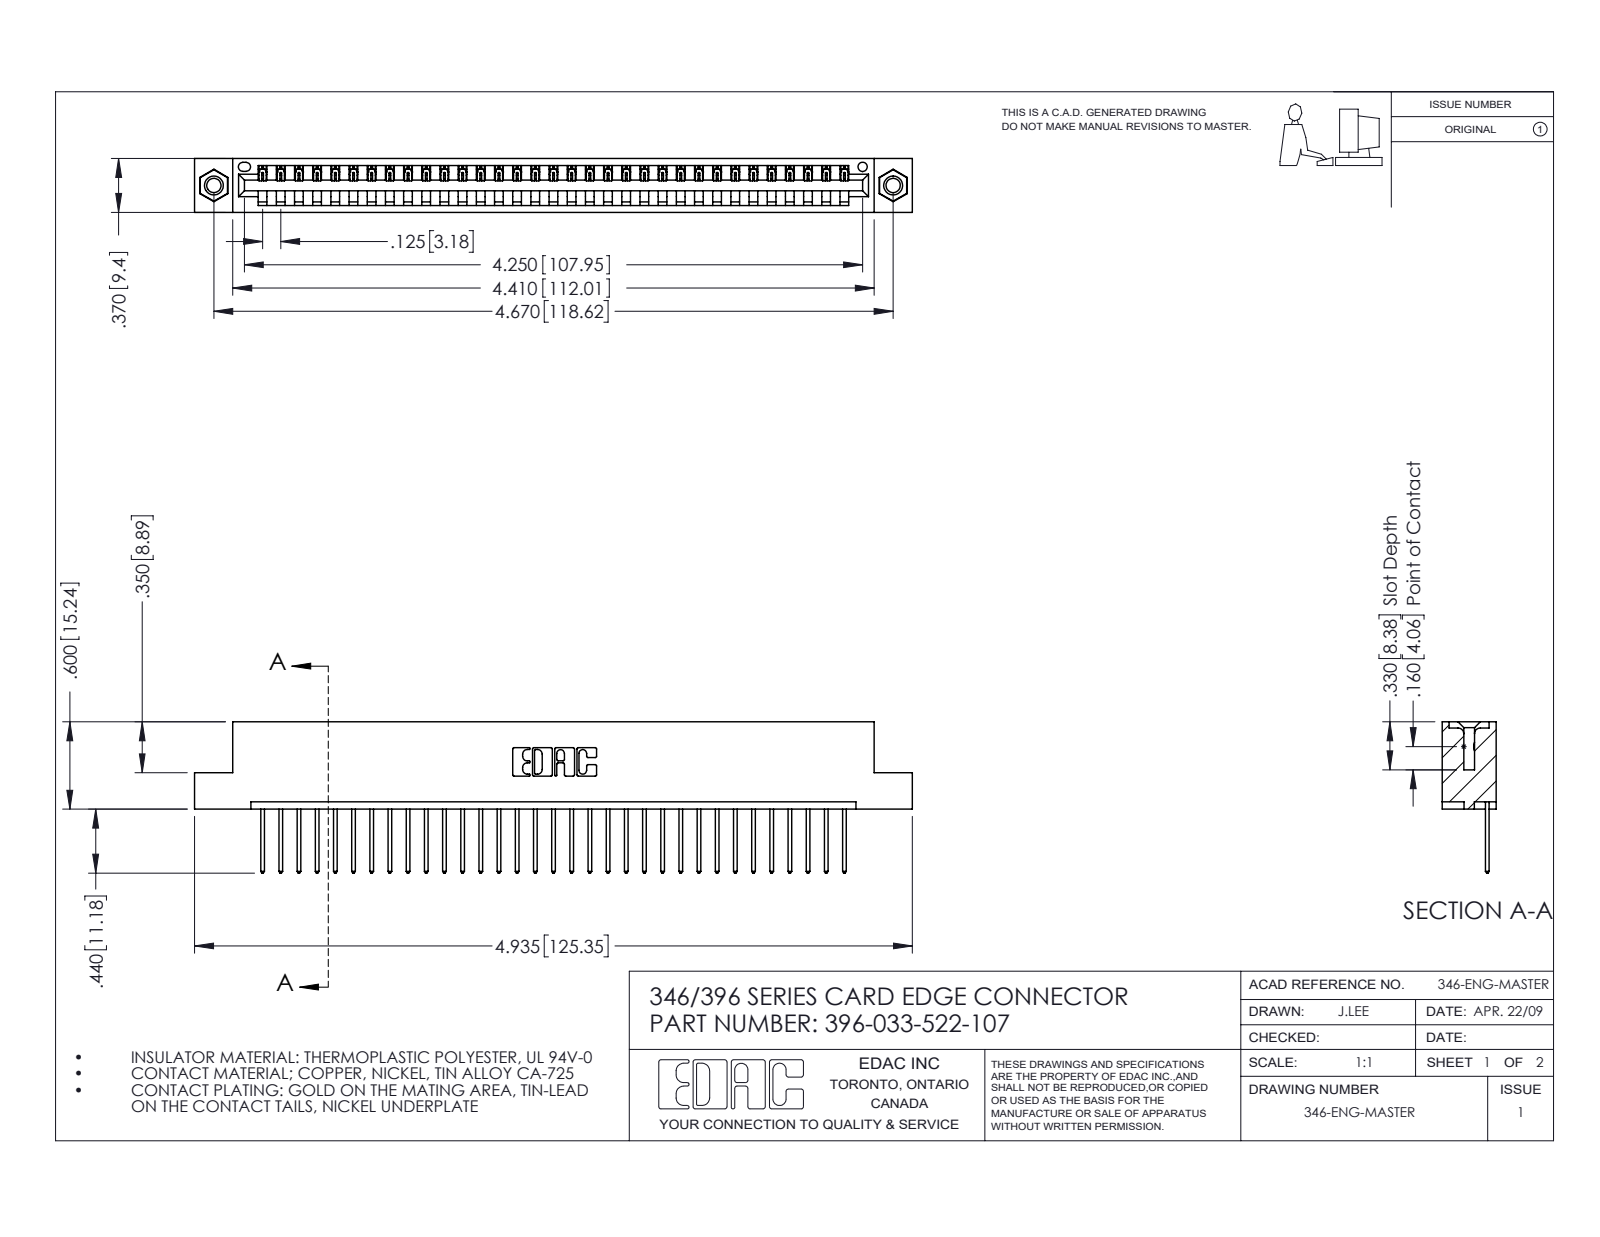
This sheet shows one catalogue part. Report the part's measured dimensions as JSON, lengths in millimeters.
{"part_name": "345-250-001_345-250-005-103; 346 Part_Flush Mounting Lugs - 0.156 Dia-TI; 396-033-522-107; 345-292-001_345-293-122", "step_written_by": "SolidWorks 2016 (CONFIG_CONTROL_DESIGN)", "units": "millimeters", "bodies": {"solids": 36, "faces": 2096, "planar": 1428, "cylindrical": 652, "other": 16}, "overall_size": [125.3, 26.4, 9.4], "volume_mm3": 11900, "surface_area_mm2": 14970, "round_holes": [[2.5, 2], [3.2, 2], [4, 2], [1.6, 1]], "round_bosses_or_shafts": [[3.9, 2]], "partial_cylinders_radius": [[0.2, 66], [0.3, 66], [0.3, 22], [0.2, 6], [0.8, 6], [0.7, 3], [0.8, 2], [1, 2]], "face_to_face_distances": [1.2, 8.2, 9.4, 6.4, 1.8, 7.6, 0.6, 3.8, 5.6, 2.5], "hole_center_spacings": [6.2, 113.3, 118.6]}
